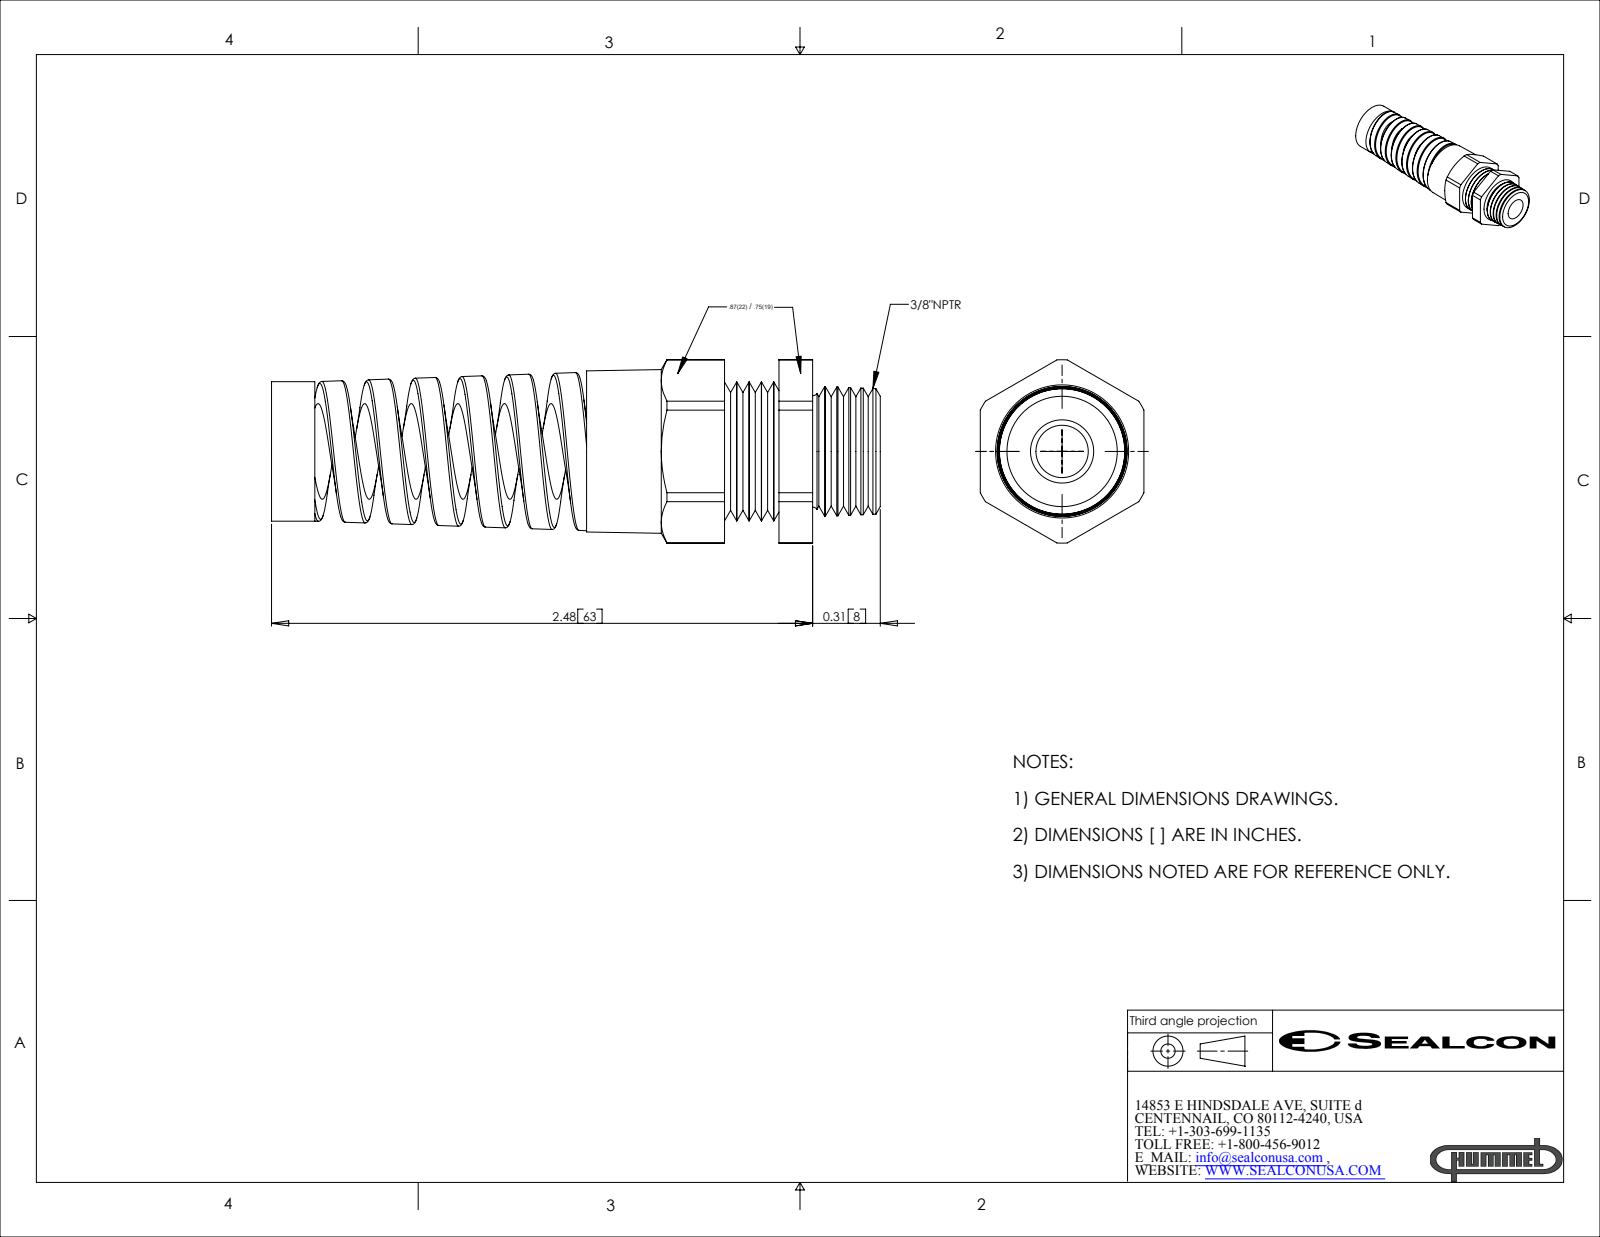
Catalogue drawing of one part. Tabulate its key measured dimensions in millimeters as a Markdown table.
| quantity | value |
| --- | --- |
| part name | CF09NR-GY |
| STEP written by | SolidWorks 2007 (CONFIG_CONTROL_DESIGN) |
| units | millimeters |
| bodies | 1 solid, 144 faces (19 planar, 40 cylindrical, 85 other) |
| overall size | 70.9 × 21.3 × 19.1 |
| volume | 10 100 mm³ |
| surface area | 7 671 mm² |
| round holes (diameter × count) | 6.1 × 1, 11.2 × 1 |
| round bosses / shafts (diameter × count) | 16.2 × 1, 16.2 × 1 |
| partial cylindrical surfaces (radius × count) | 10.7 × 1 |
| main face-to-face distances | 19.1, 26.3, 36.7, 63, 59.1, 22.4, 3.9, 52.7, 16.1, 6.4 |
